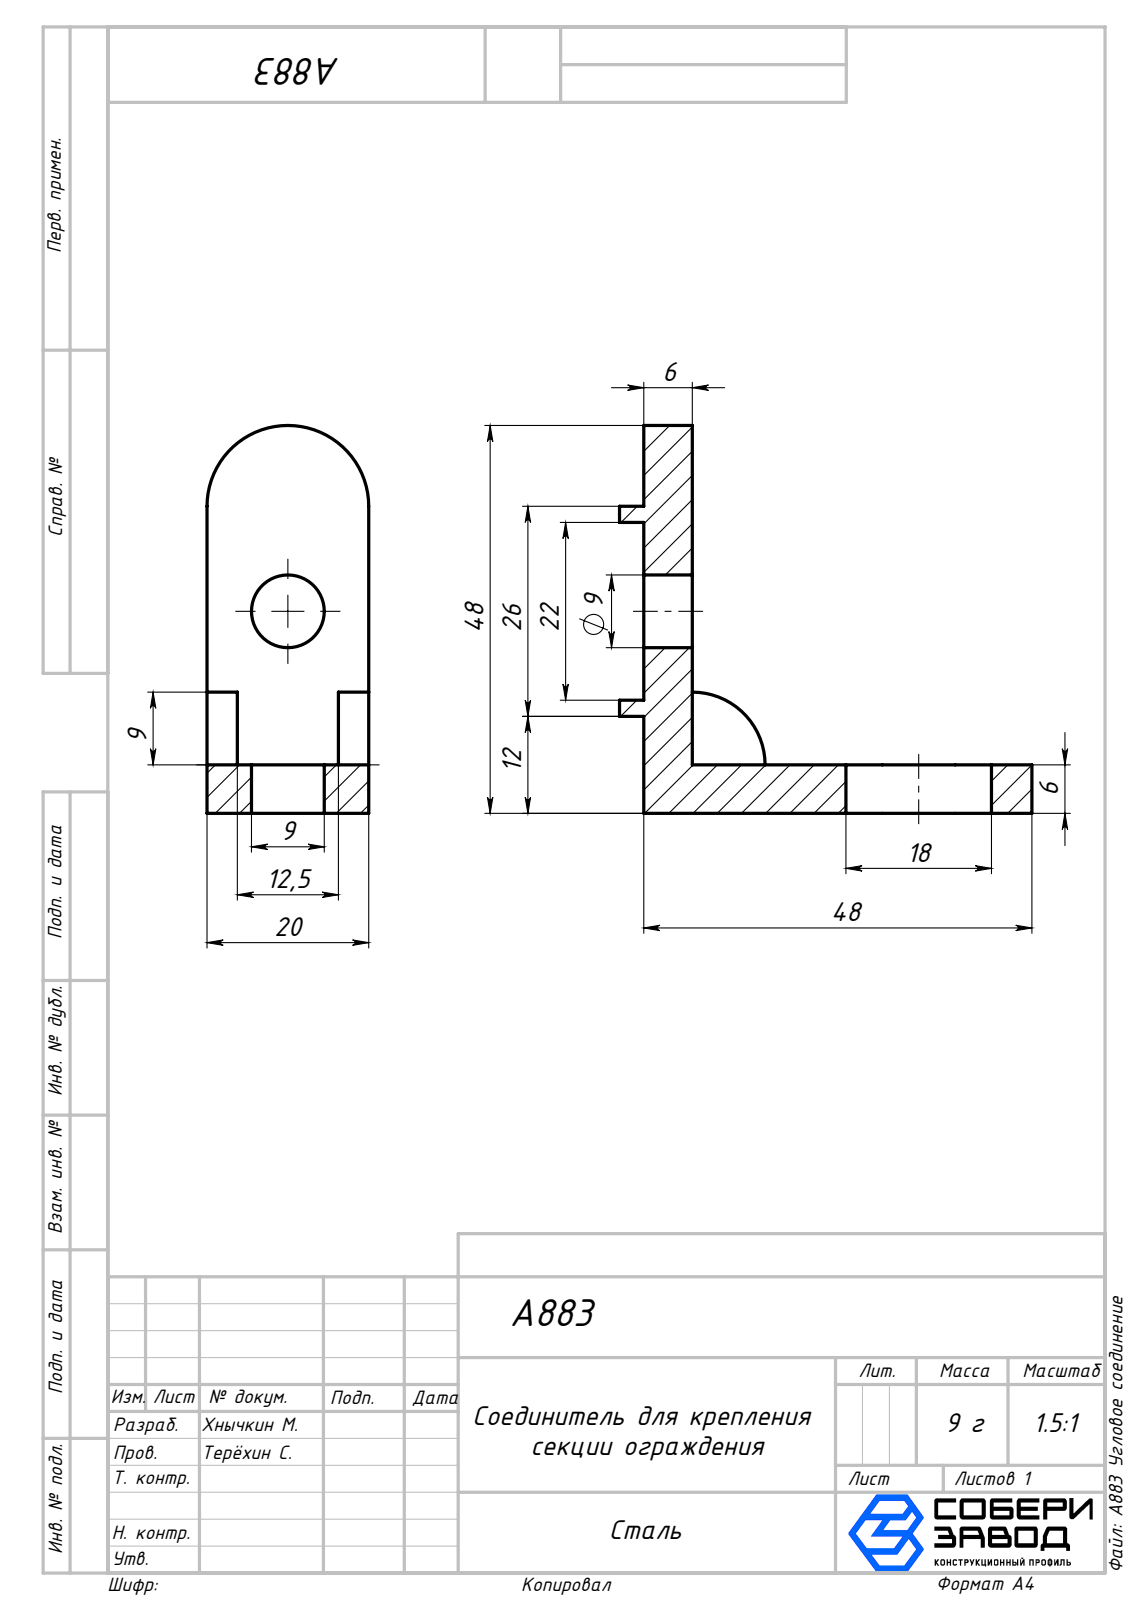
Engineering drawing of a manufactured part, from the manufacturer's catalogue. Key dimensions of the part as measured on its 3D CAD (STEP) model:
Part name (STEP PRODUCT): A883 Угловое соединение
STEP written by: SolidWorks 2025 (AUTOMOTIVE_DESIGN)
Units: millimetres
Bodies: 1 solid, 31 faces (20 planar, 11 cylindrical, 0 other)
Overall size (bounding box): 51 × 48 × 20
Volume: 9 633 mm³ · Surface area: 5 046 mm²
Round holes (diameter × count): ⌀9 ×1
Partial cylindrical surfaces — rounded edges, fillets, slot ends (radius × count): R4.5 ×2, R10 ×2, R9 ×1
Main face-to-face distances: 6, 20, 3.75, 16.25, 5.5, 14.5, 1.75, 10.75, 9, 12.5
